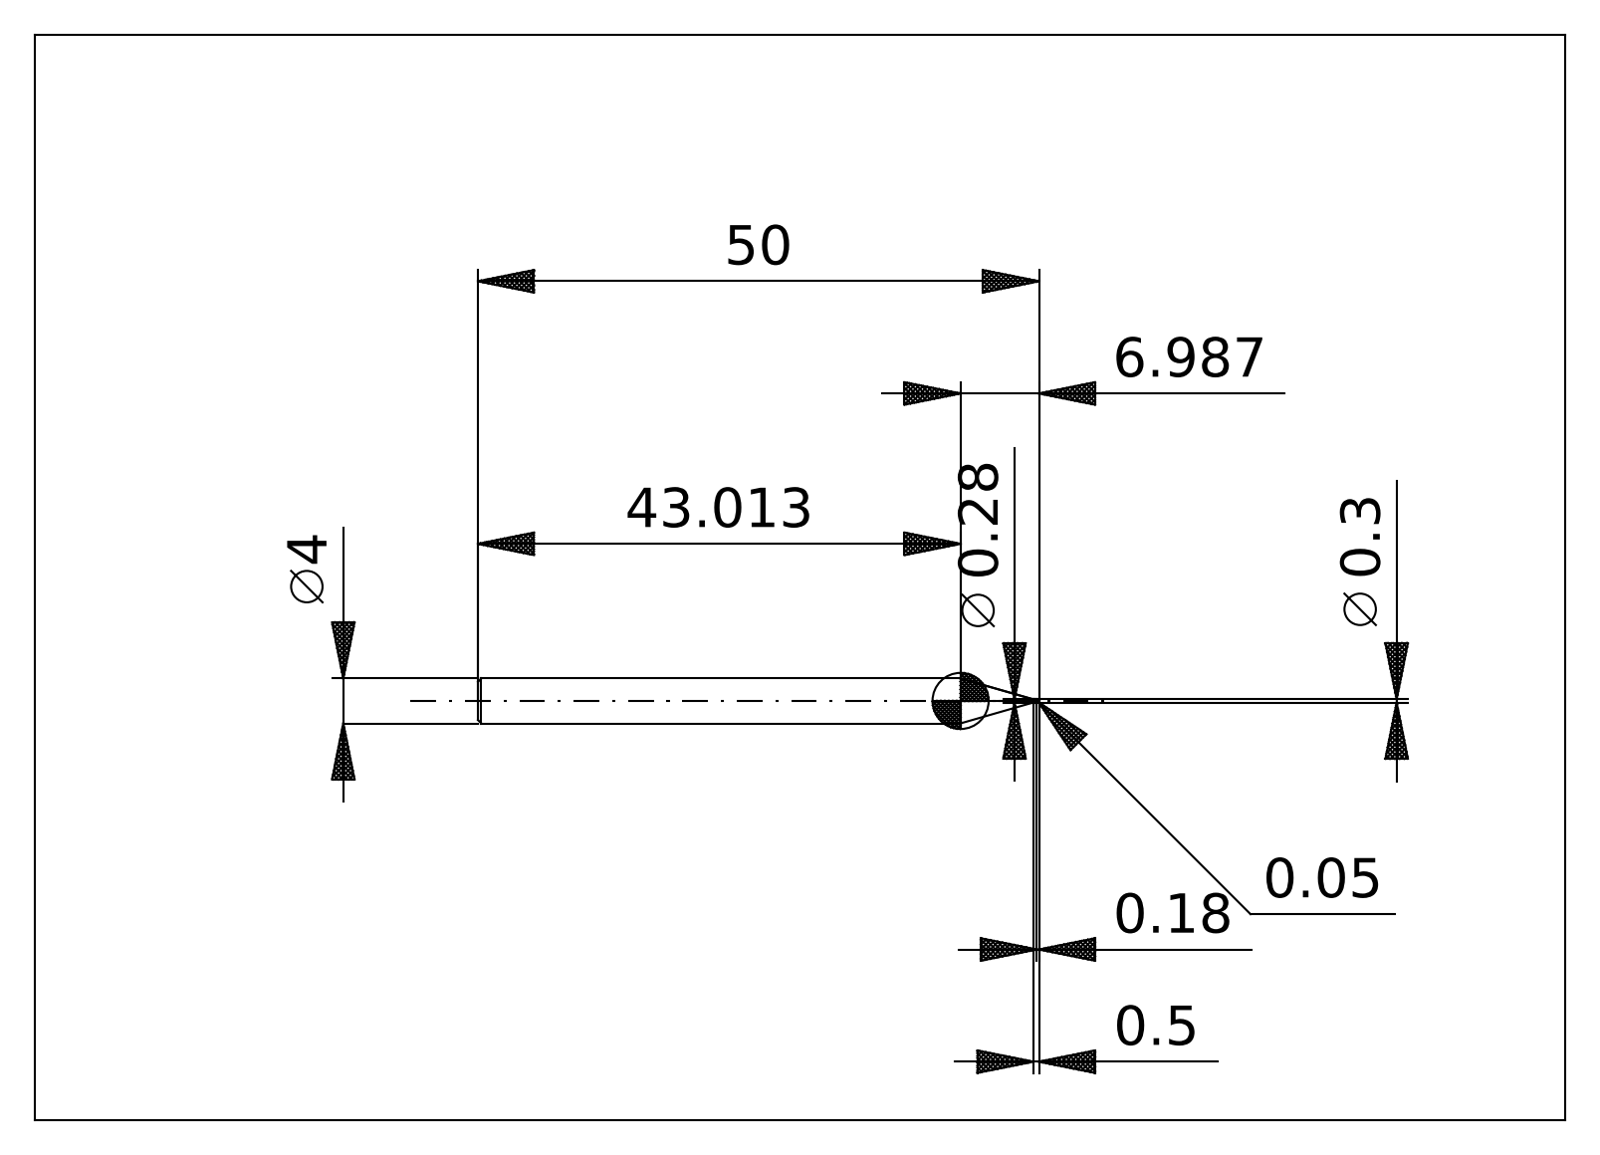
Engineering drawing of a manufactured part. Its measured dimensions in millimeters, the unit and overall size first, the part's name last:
Units: millimetres
Overall size (bounding box): 50 × 4 × 4
Round bosses / shafts (diameter × count): ⌀4 ×1, ⌀0.28 ×1
Main face-to-face distances: 50, 49.96, 49.82, 6.99, 6.95, 6.81, 43.01
Volume: 569 mm³ · Surface area: 597 mm²
Bodies: 2 solids, 26 faces (6 planar, 8 cylindrical, 12 other)
STEP written by: ACIS (automotive_design)
